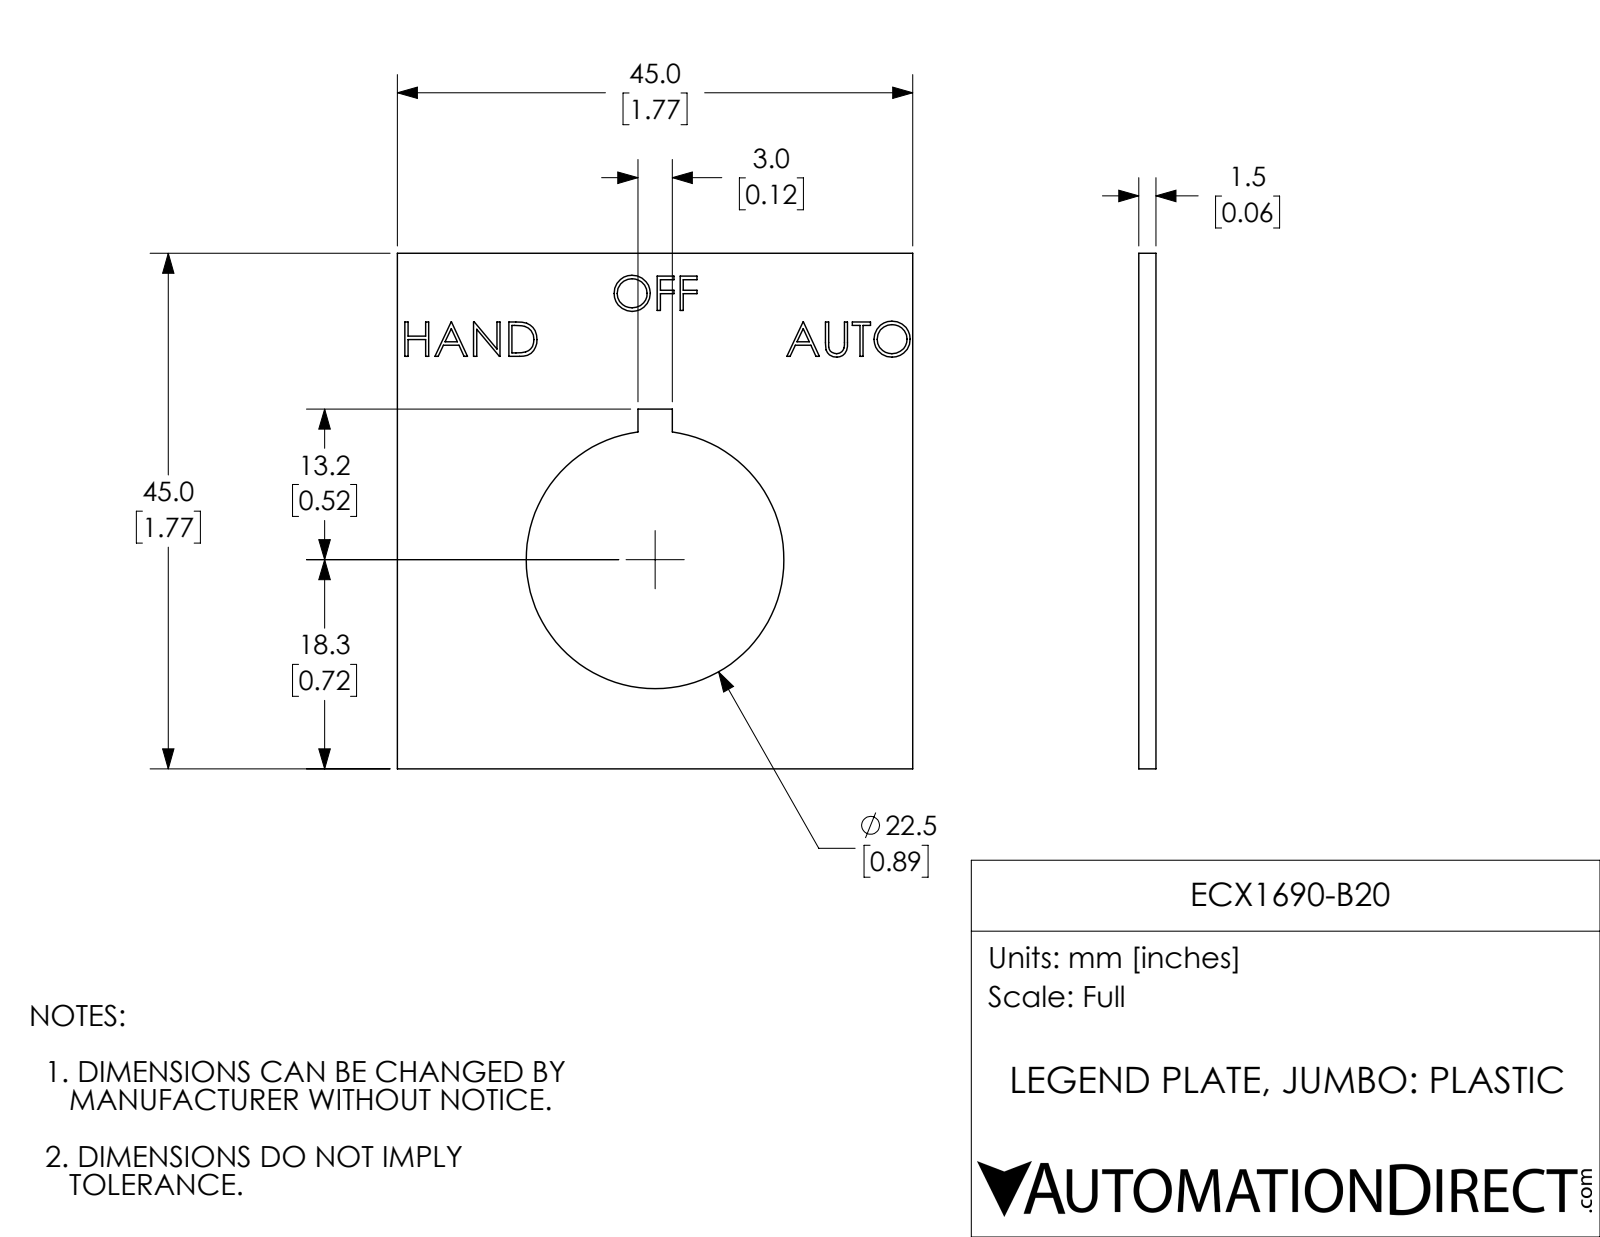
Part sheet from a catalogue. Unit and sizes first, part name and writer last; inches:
Units: inches
Overall size (bounding box): 1.772 × 1.772 × 0.059
Round holes (diameter × count): ⌀0.886 ×1
Main face-to-face distances: 0.059, 1.772, 0.058, 0.827, 0.945, 1.236, 0.535, 0.118, 0.236, 0.079
Volume: 0.148 in³ · Surface area: 5.625 in²
Bodies: 1 solid, 142 faces (109 planar, 3 cylindrical, 30 other)
Part name (STEP PRODUCT): ECX1690-B20
STEP written by: SolidWorks 2018 (AUTOMOTIVE_DESIGN)
